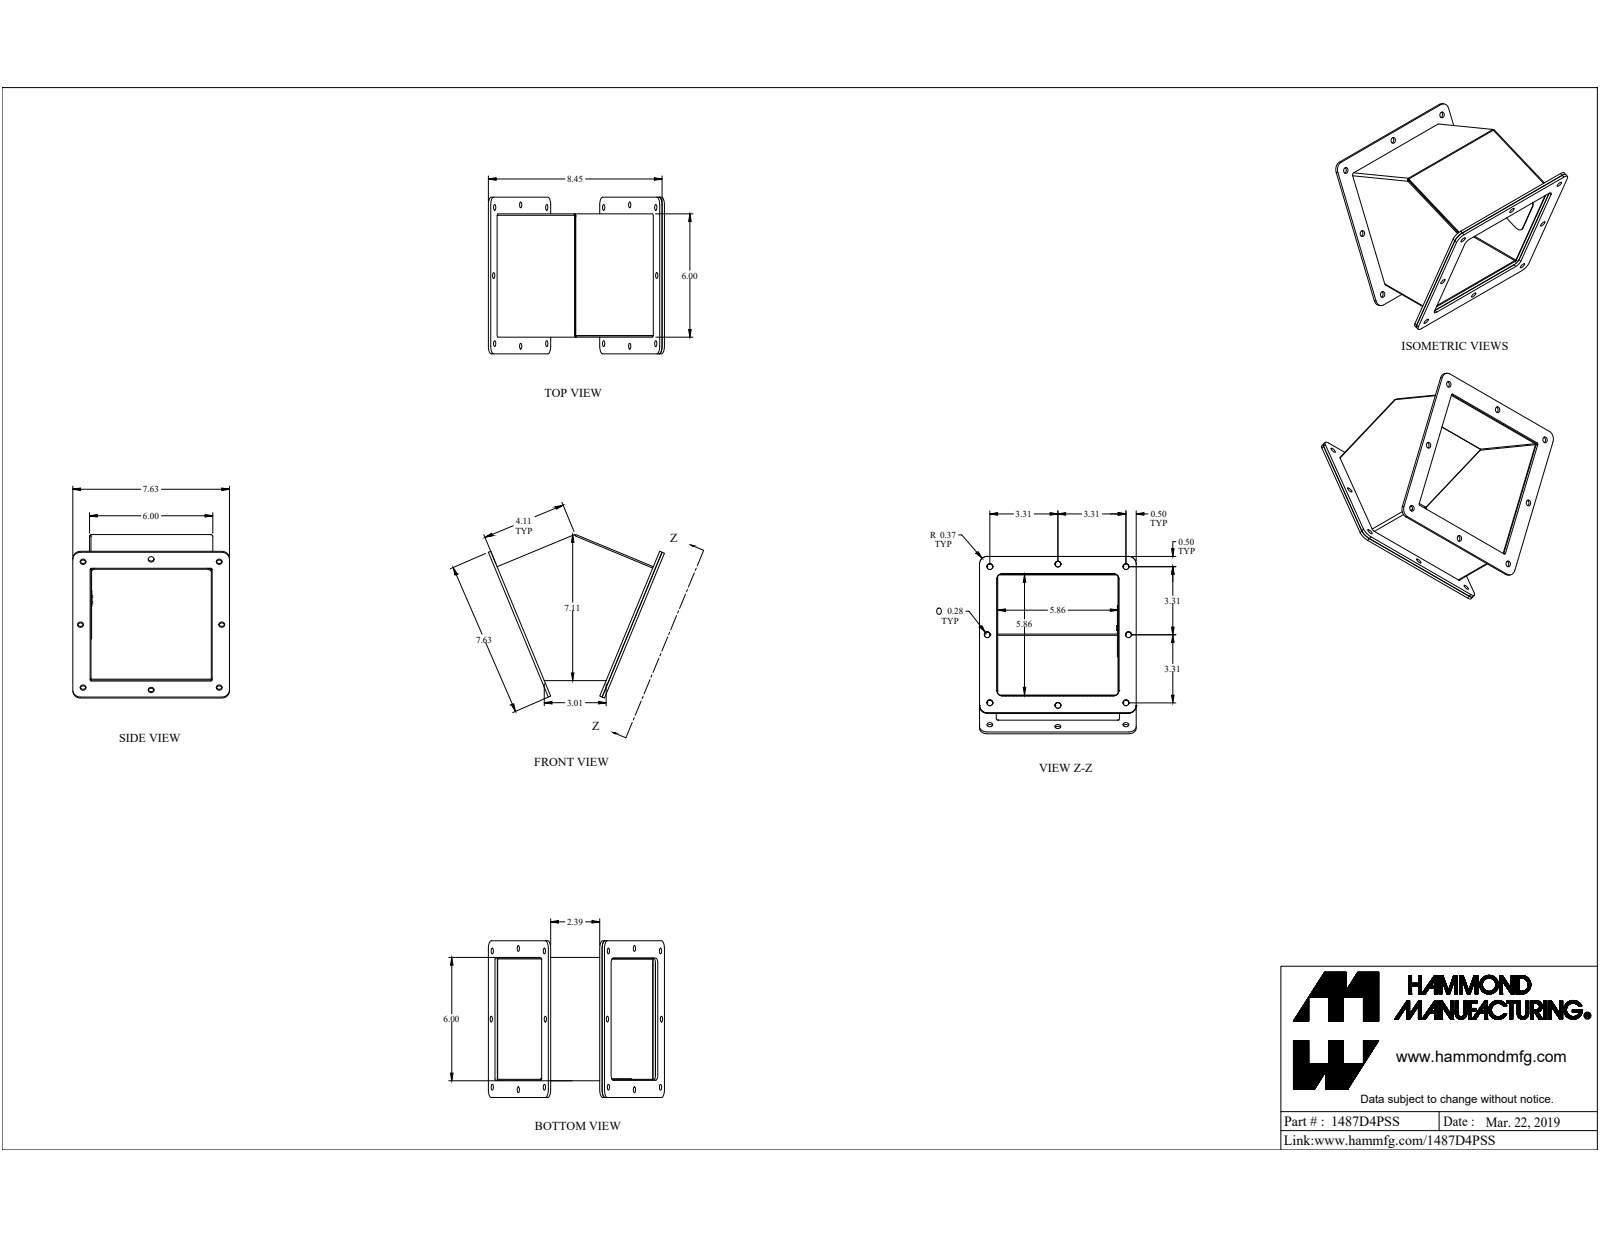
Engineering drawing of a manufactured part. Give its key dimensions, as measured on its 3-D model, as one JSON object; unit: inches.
{"part_name": "1487D4PSS", "step_written_by": "SolidWorks 2021 (AUTOMOTIVE_DESIGN)", "units": "inches", "bodies": {"solids": 6, "faces": 189, "planar": 99, "cylindrical": 82, "other": 8}, "overall_size": [8.654, 7.964, 7.625], "volume_in3": 18.23, "surface_area_in2": 433.9, "round_holes": [[0.281, 24], [0.196, 1], [0.35, 1], [0.5, 1]], "round_bosses_or_shafts": [[0.25, 1]], "partial_cylinders_radius": [[0.063, 8], [0.375, 8], [0.02, 6], [0.036, 6], [0.108, 6], [0.25, 4]], "face_to_face_distances": [0.072, 5.928, 0.125, 5.856, 6, 0.125, 0.25, 0.813, 0.885, 6.741], "hole_center_spacings": [3.315, 7.519, 6.625, 3.315, 4.861, 6.875, 9.369, 7.522]}
